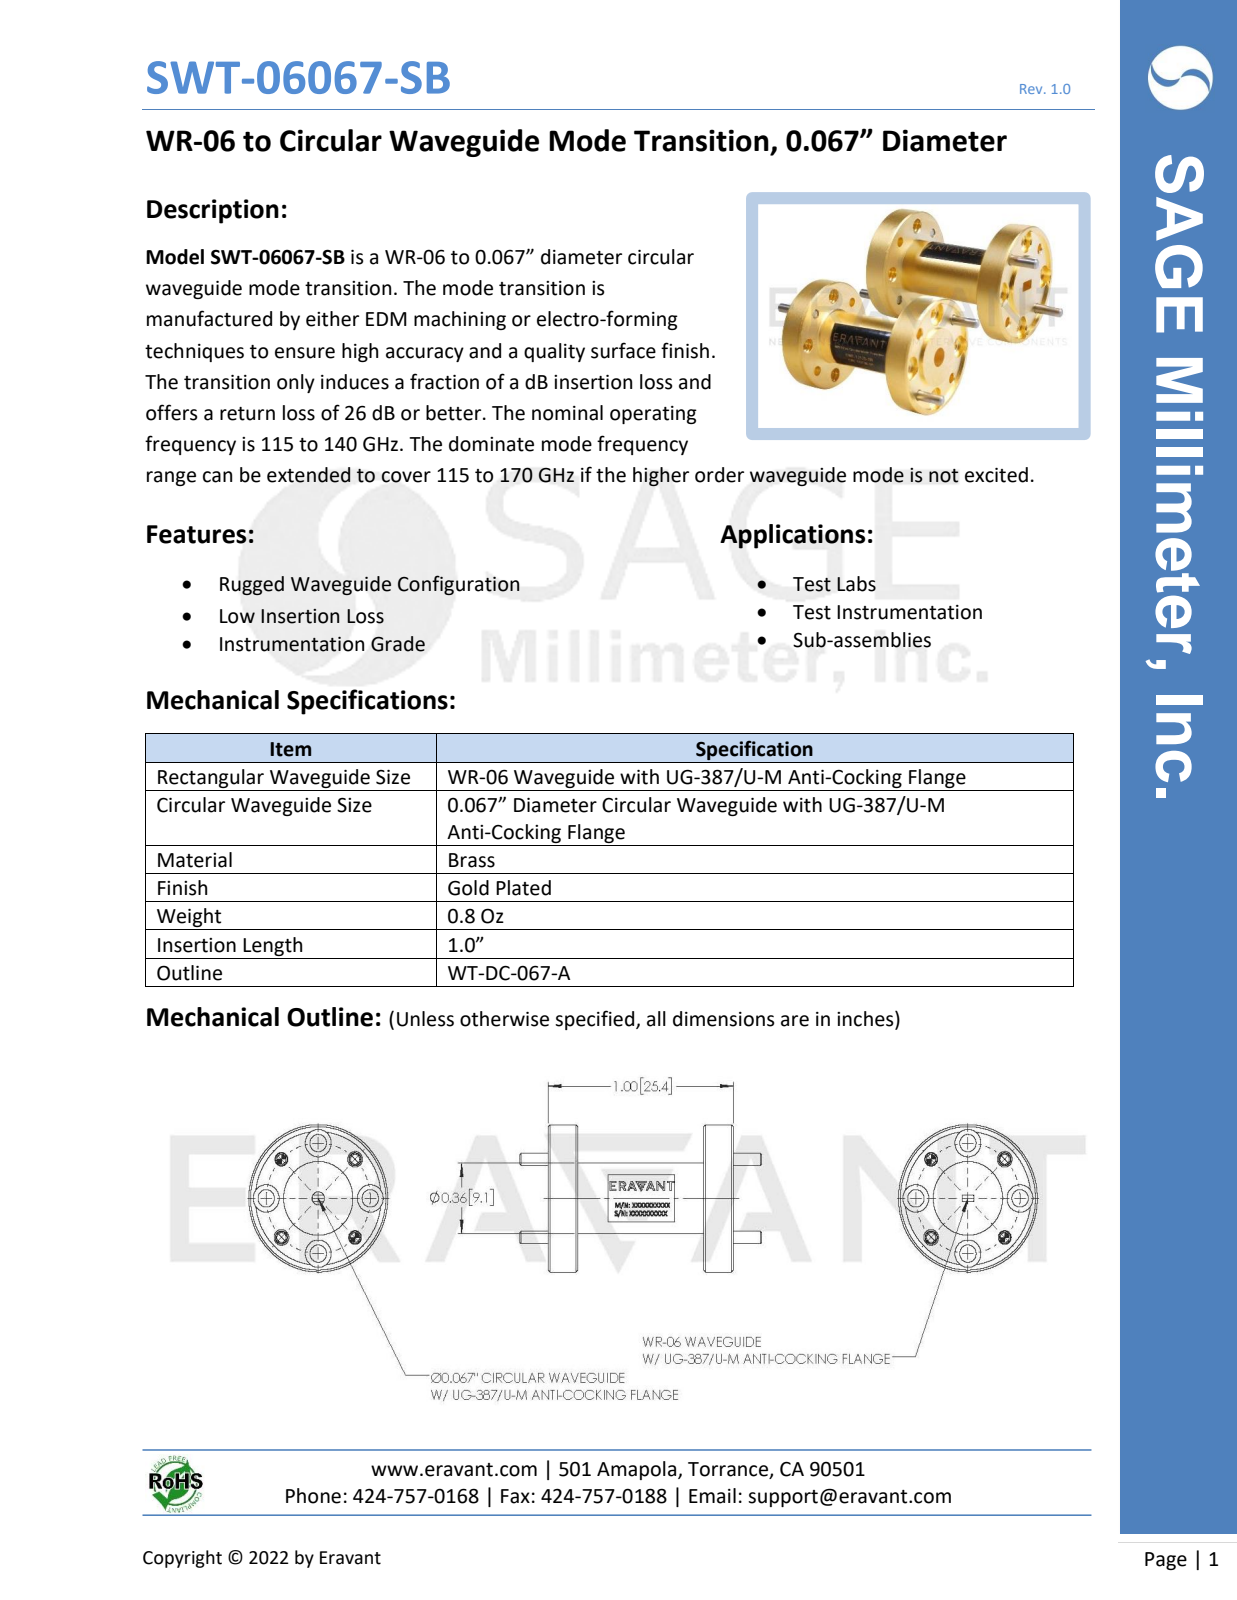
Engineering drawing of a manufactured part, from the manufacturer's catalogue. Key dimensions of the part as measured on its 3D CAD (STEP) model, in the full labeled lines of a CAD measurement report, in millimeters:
Part name (STEP PRODUCT): WT-DC-067-A Defeatured
STEP written by: SolidWorks 2021 (AUTOMOTIVE_DESIGN)
Units: millimetres
Bodies: 5 solids, 148 faces (26 planar, 74 cylindrical, 48 other)
Overall size (bounding box): 33.1 × 19.1 × 19.1
Volume: 3 110 mm³ · Surface area: 2 494 mm²
Round holes (diameter × count): ⌀1.5 ×4, ⌀1.7 ×4, ⌀2.3 ×4, ⌀3.6 ×4, ⌀17.3 ×1
Round bosses / shafts (diameter × count): ⌀1.6 ×4, ⌀19.1 ×1, ⌀9.5 ×1, ⌀9.5 ×1, ⌀9.1 ×1
Main face-to-face distances: 24.9, 0.5, 17.3, 20.8, 3.6, 3.6, 20.8, 24.4, 21.3, 4.1
Hole centre spacings: 5.5, 10.1, 7.1, 13.2, 14.3, 13.2, 7.1, 14.3
